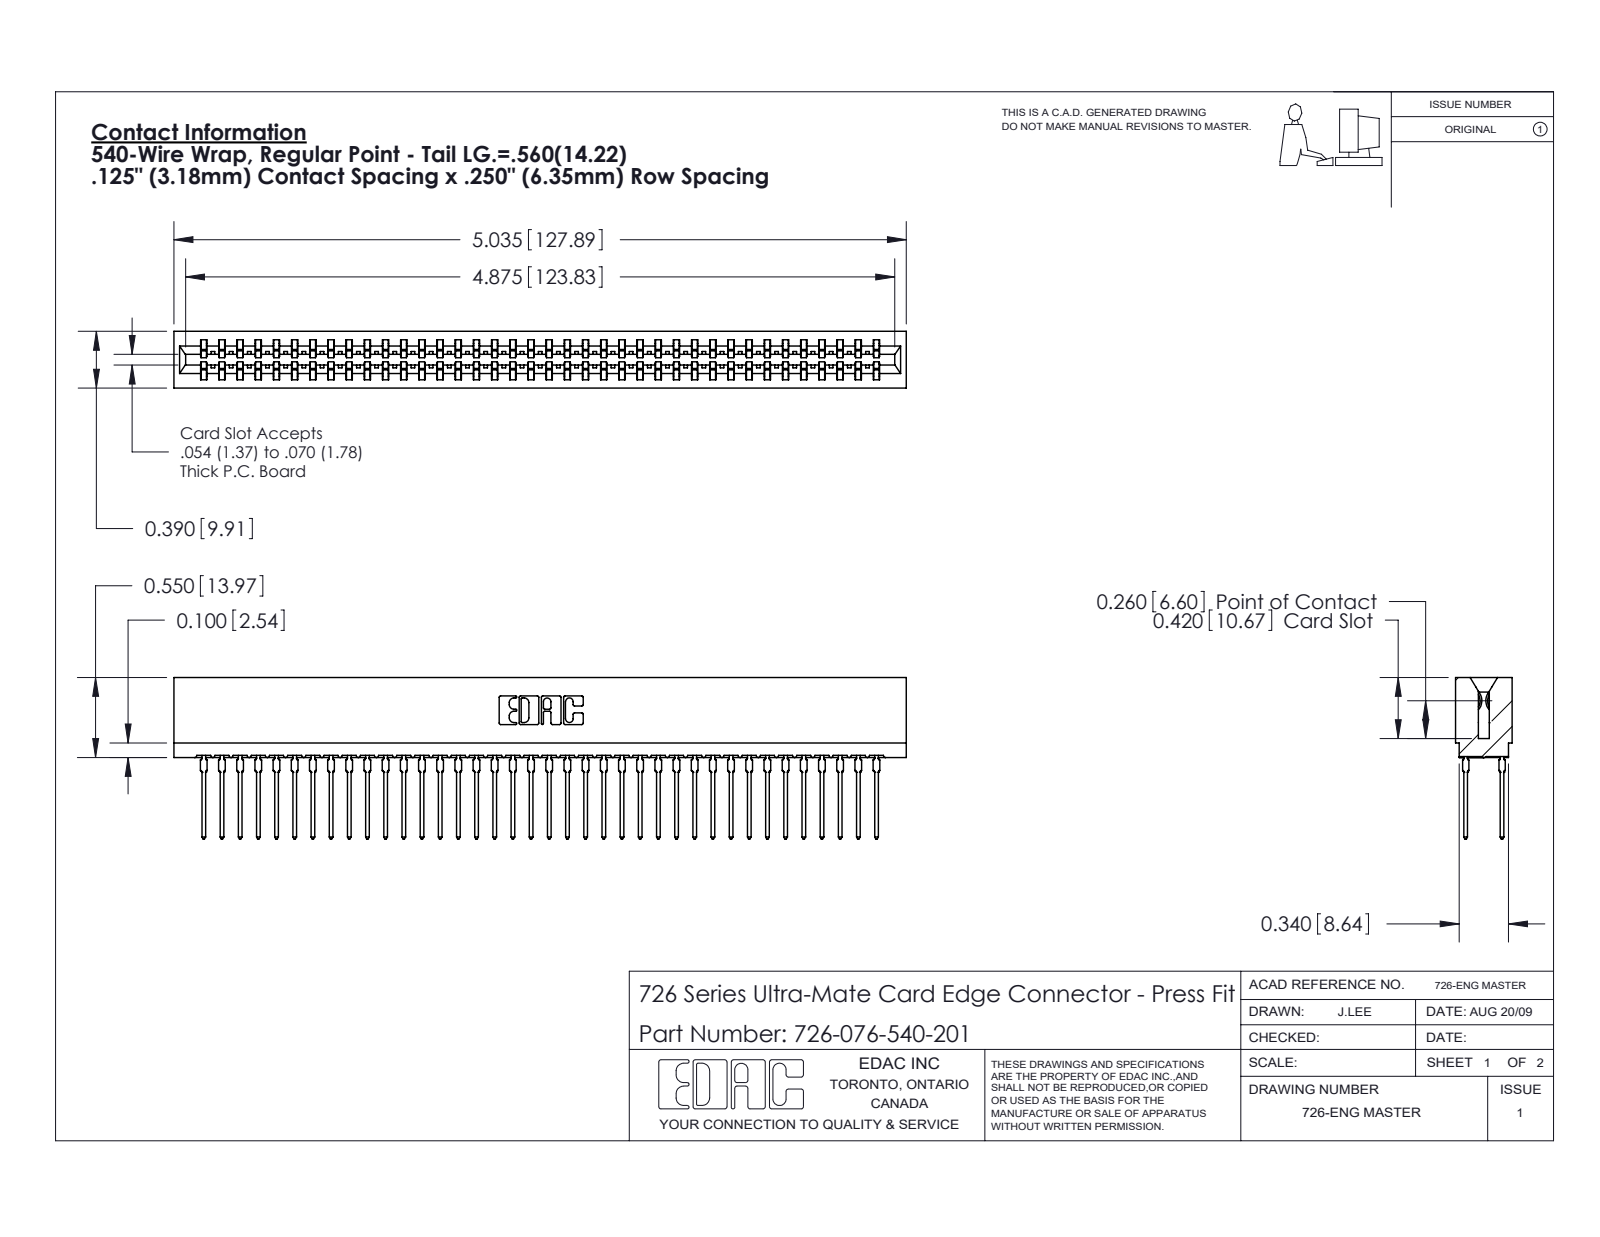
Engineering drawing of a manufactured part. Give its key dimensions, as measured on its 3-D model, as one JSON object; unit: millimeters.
{"part_name": "746-292-001_540; 726-076-540-201; 726 Part_.515 Slot Depth - 01", "step_written_by": "SolidWorks 2020 (CONFIG_CONTROL_DESIGN)", "units": "millimeters", "bodies": {"solids": 77, "faces": 6899, "planar": 3551, "cylindrical": 1372, "other": 1976}, "overall_size": [127.9, 28.2, 9.9], "volume_mm3": 12000, "surface_area_mm2": 21030, "partial_cylinders_radius": [[0.5, 152], [0.4, 39], [0.3, 22], [0.1, 8], [0.3, 8], [0.2, 6], [0.8, 6], [0.7, 3]], "face_to_face_distances": [1.4, 8.5, 6.4, 0.6, 7.8, 9.9, 2.1, 7, 12.7, 9.3]}
